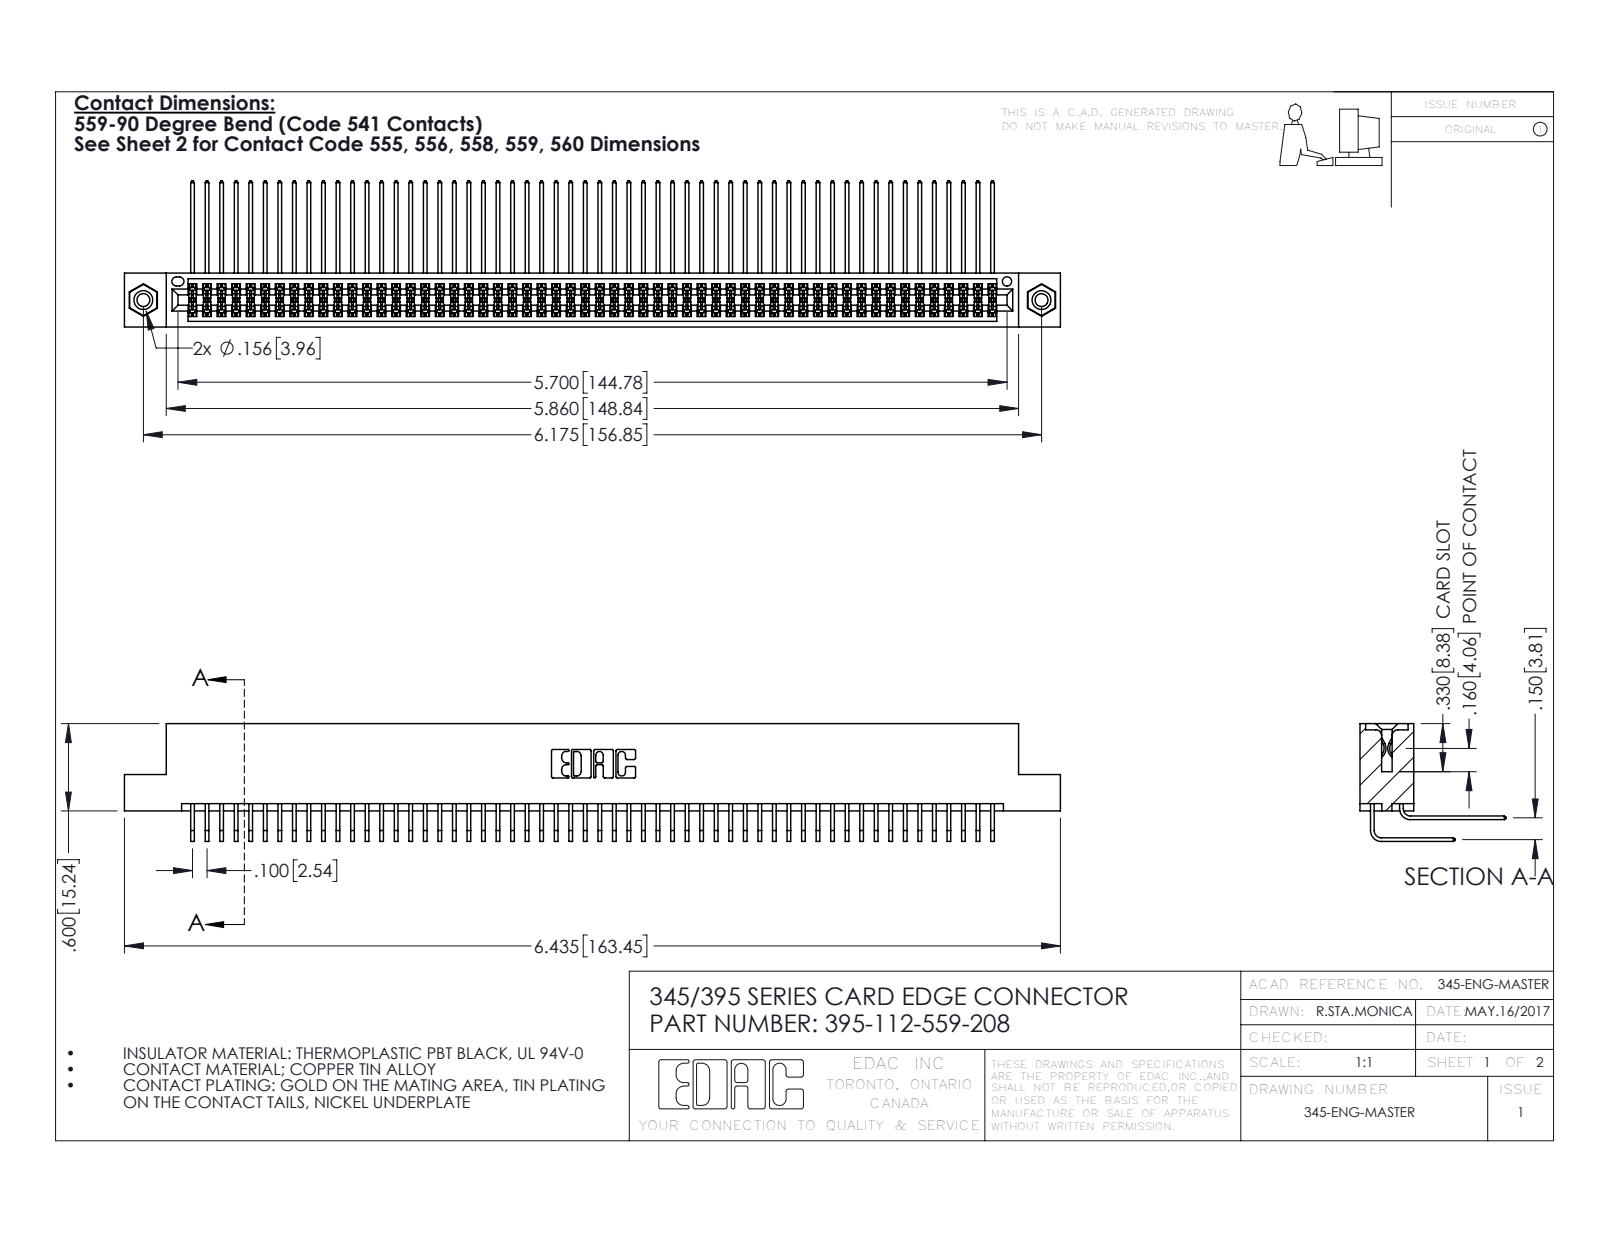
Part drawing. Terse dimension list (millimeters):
name: 345-292-001_559 Tail - 2; 345 Part_Flush Mounting Lugs - 0.156 Dia-TI; 395-112-559-208; 345-292-001_558 559 Tail - 1 (+1 more)
written by: SolidWorks 2016 (CONFIG_CONTROL_DESIGN)
unit: mm
bodies: 115 solids, 6010 faces (4032 planar, 1962 cylindrical, 16 other)
size: 163.4 × 25.5 × 20.5
volume: 16 650 mm³; area: 27 930 mm²
holes: 2× ⌀2.3, 2× ⌀3.2, 2× ⌀4, 1× ⌀1.6
bosses: 2× ⌀3.9
rounds: 168× R0.2, 22× R0.3, 6× R0.2, 6× R0.8, 3× R0.7, 2× R0.4, 2× R0.5, 2× R0.6
face distances: 1.8, 7.6, 5.1, 9.4, 2.5, 6.9, 0.6, 5.7, 4.4, 3.8
hole spacings: 6.9, 150.9, 156.8
